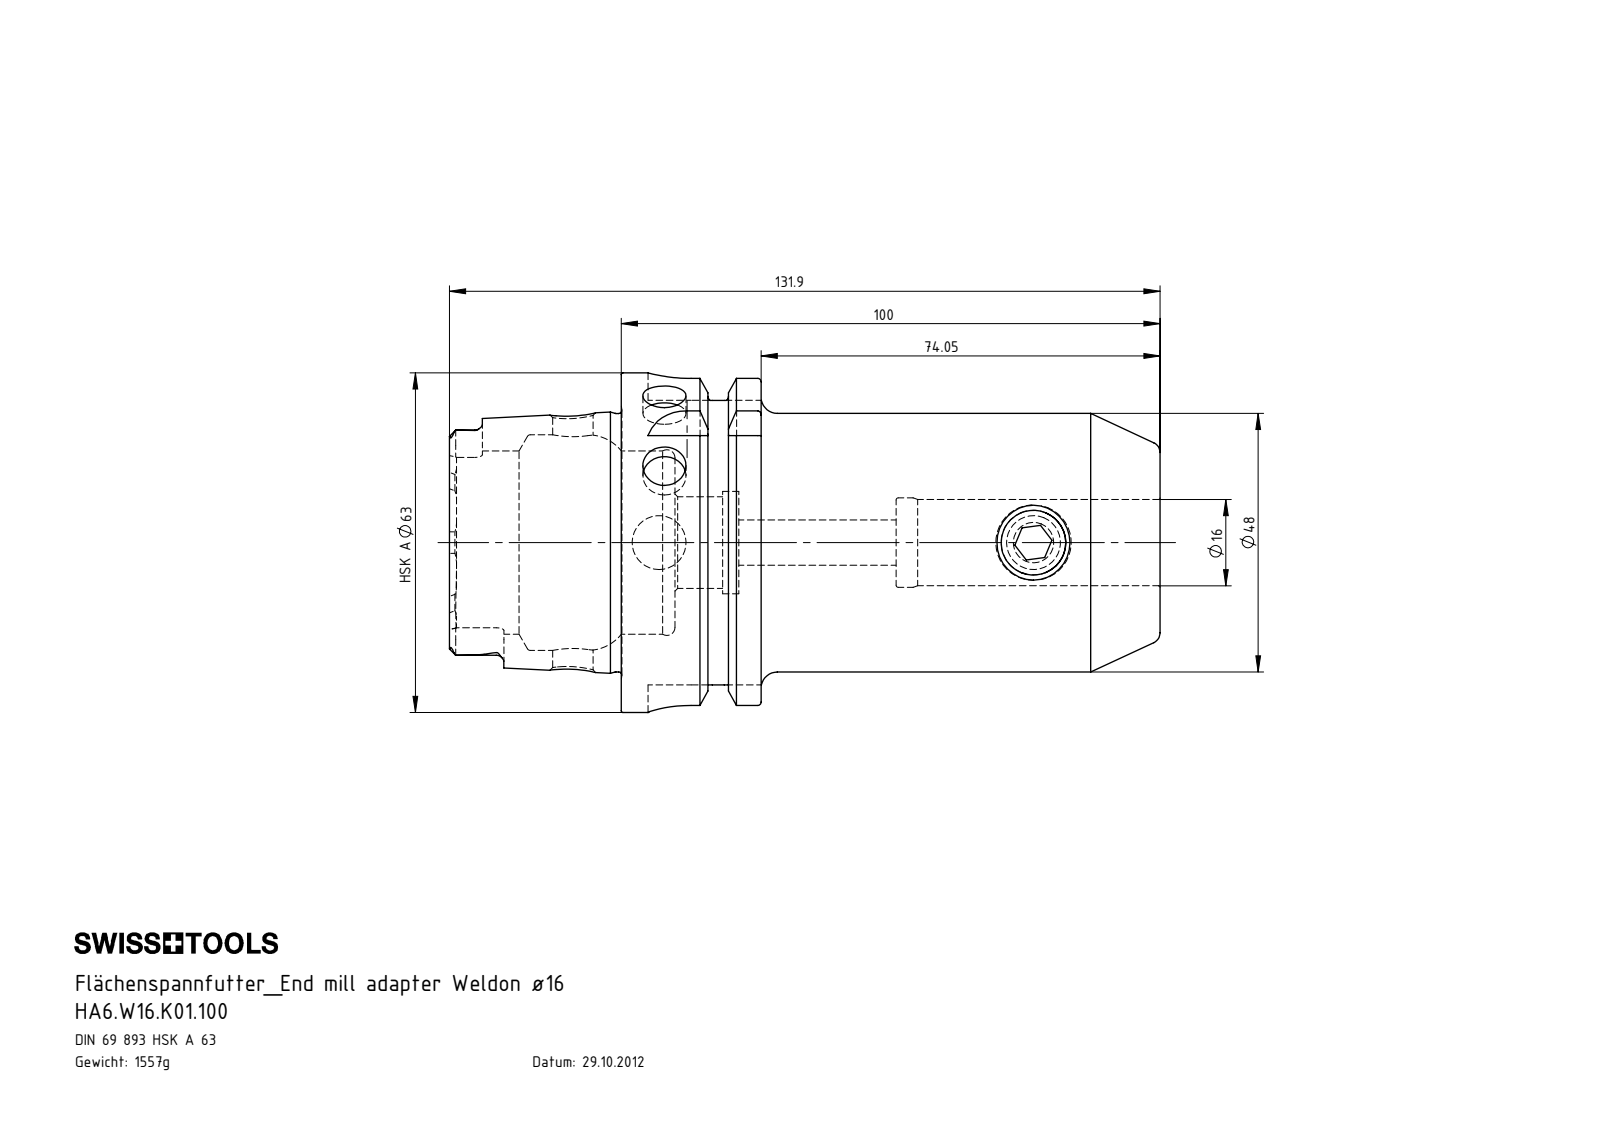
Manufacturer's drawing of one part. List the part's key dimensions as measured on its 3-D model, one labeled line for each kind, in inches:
Part name (STEP PRODUCT): W16-ER1.001.016; HA6-W16.K01.100_A_Fertigbearbeitung; HA6-W16.K01.100
STEP written by: SolidWorks 2012 (CONFIG_CONTROL_DESIGN)
Units: inches
Bodies: 2 solids, 209 faces (59 planar, 57 cylindrical, 93 other)
Overall size (bounding box): 5.193 × 2.48 × 2.48
Volume: 12.1 in³ · Surface area: 57.7 in²
Round holes (diameter × count): ⌀0.315 ×2, ⌀0.295 ×1, ⌀0.331 ×1, ⌀0.394 ×1, ⌀0.472 ×1, ⌀0.63 ×1, ⌀0.654 ×1, ⌀0.669 ×1, ⌀0.748 ×1, ⌀1.339 ×1, ⌀1.575 ×1
Round bosses / shafts (diameter × count): ⌀2.48 ×1, ⌀2.163 ×1, ⌀1.89 ×1, ⌀1.887 ×1, ⌀0.551 ×1
Partial cylindrical surfaces — rounded edges, fillets, slot ends (radius × count): R0.055 ×6, R0.113 ×4, R0.315 ×4
Main face-to-face distances: 3.937, 1.022, 2.915, 0.63, 0.392, 3.545, 1.256, 1.648, 2.278, 5.193
Hole centre spacings: 2.736
